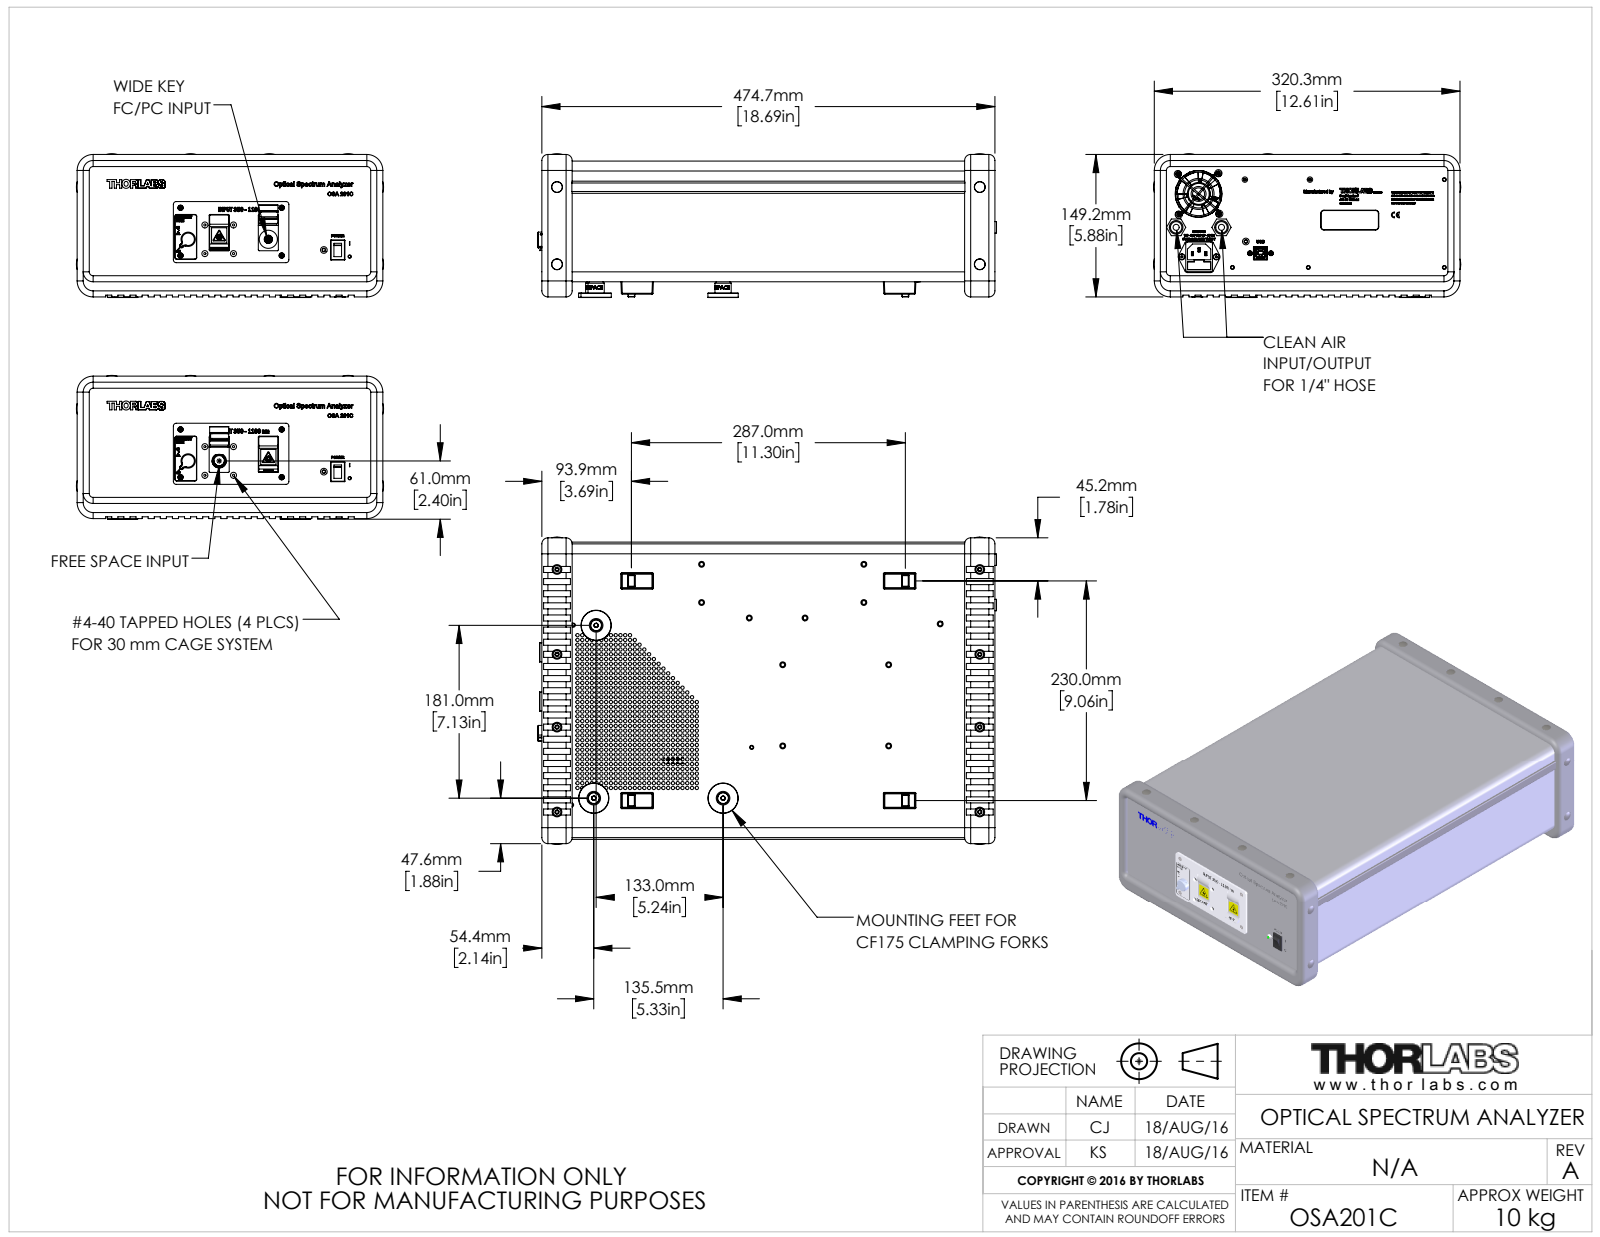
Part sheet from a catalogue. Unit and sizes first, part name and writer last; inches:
Units: inches
Overall size (bounding box): 18.933 × 12.67 × 5.941
Round holes (diameter × count): ⌀0.138 ×749, ⌀0.098 ×37, ⌀0.081 ×26, ⌀0.13 ×19, ⌀0.168 ×14, ⌀0.089 ×13, ⌀0.047 ×12, ⌀0.2 ×12, ⌀0.45 ×12, ⌀0.118 ×11, ⌀0.122 ×9, ⌀0.126 ×9
Round bosses / shafts (diameter × count): ⌀0.118 ×26, ⌀0.197 ×16, ⌀0.157 ×16, ⌀0.094 ×13, ⌀0.435 ×12, ⌀0.256 ×11, ⌀0.059 ×11, ⌀0.311 ×8
Partial cylindrical surfaces — rounded edges, fillets, slot ends (radius × count): R0.02 ×91, R0.039 ×57, R0.059 ×49, R0.118 ×39, R0.006 ×24, R0.022 ×24, R0.061 ×22, R0.063 ×21
Main face-to-face distances: 0.039, 4.941, 4.98, 4.902, 12.071, 3.551, 1.39, 18.15, 12.11, 12.031
Hole centre spacings: 0.197, 0.394, 0.591, 0.787, 0.984, 1.26, 0.278, 1.181
Volume: 113.4 in³ · Surface area: 2 440 in²
Bodies: 169 solids, 20196 faces (8311 planar, 5453 cylindrical, 6432 other)
Part name (STEP PRODUCT): KON 201 5151; MKD 110 0272_FC-PC; DME 103 0020; OMS 110 0055-3_Flytande (+8 more)
STEP written by: SolidWorks 2016 (AUTOMOTIVE_DESIGN)
